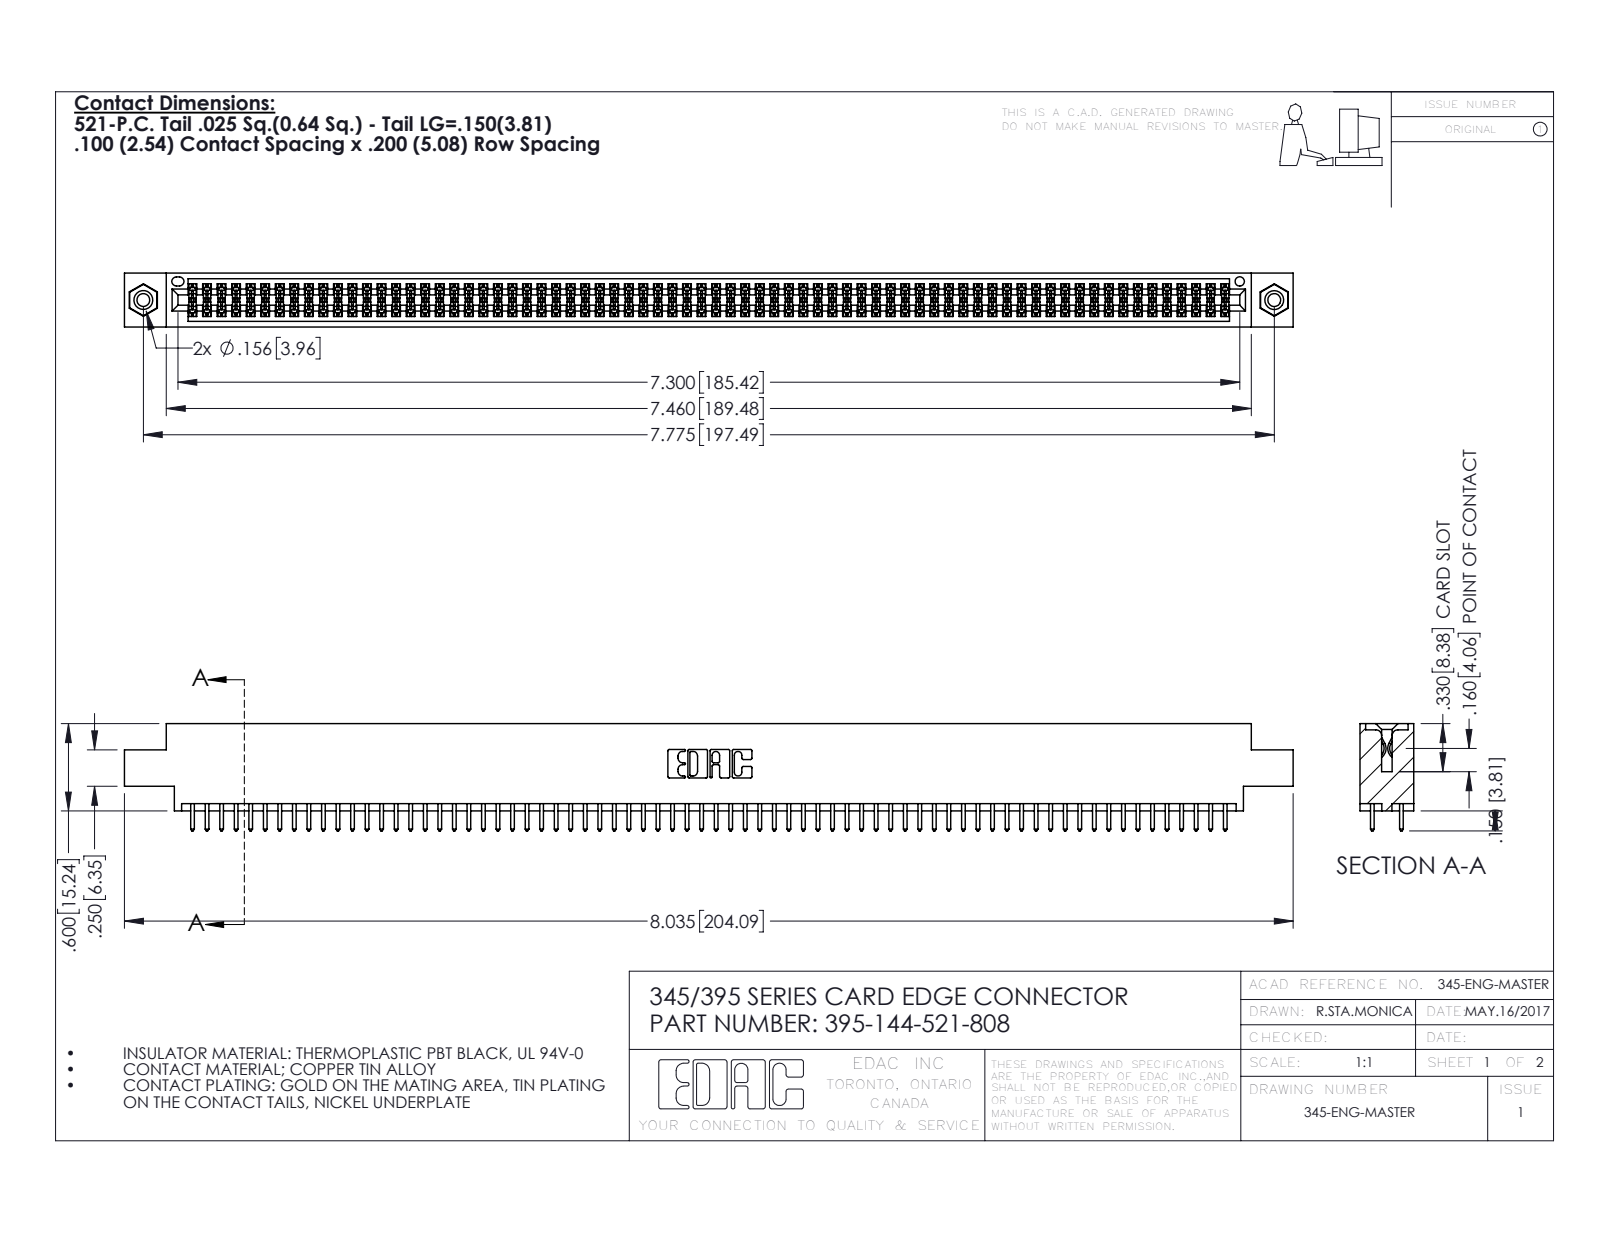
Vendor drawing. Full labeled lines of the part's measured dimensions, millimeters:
Part name (STEP PRODUCT): 345 Part_0.170 Offset - 0.156 Dia-TI; 345-292-001_345-293-121; 395-144-521-808; 345-250-001_345-250-003-102
STEP written by: SolidWorks 2016 (CONFIG_CONTROL_DESIGN)
Units: millimetres
Bodies: 147 solids, 7390 faces (4868 planar, 2506 cylindrical, 16 other)
Overall size (bounding box): 204.1 × 18.7 × 9.4
Volume: 19 930 mm³ · Surface area: 29 810 mm²
Round holes (diameter × count): ⌀2.3 ×2, ⌀3.2 ×2, ⌀4 ×2, ⌀1.6 ×1
Round bosses / shafts (diameter × count): ⌀3.9 ×2
Partial cylindrical surfaces — rounded edges, fillets, slot ends (radius × count): R0.2 ×216, R0.3 ×144, R0.3 ×22, R0.2 ×6, R0.8 ×6, R0.7 ×3, R0.4 ×2, R0.5 ×2
Main face-to-face distances: 1.8, 7.6, 5.1, 9.4, 2.5, 6.9, 0.6, 5.7, 4.4, 3.8
Hole centre spacings: 6.9, 191.5, 197.5
